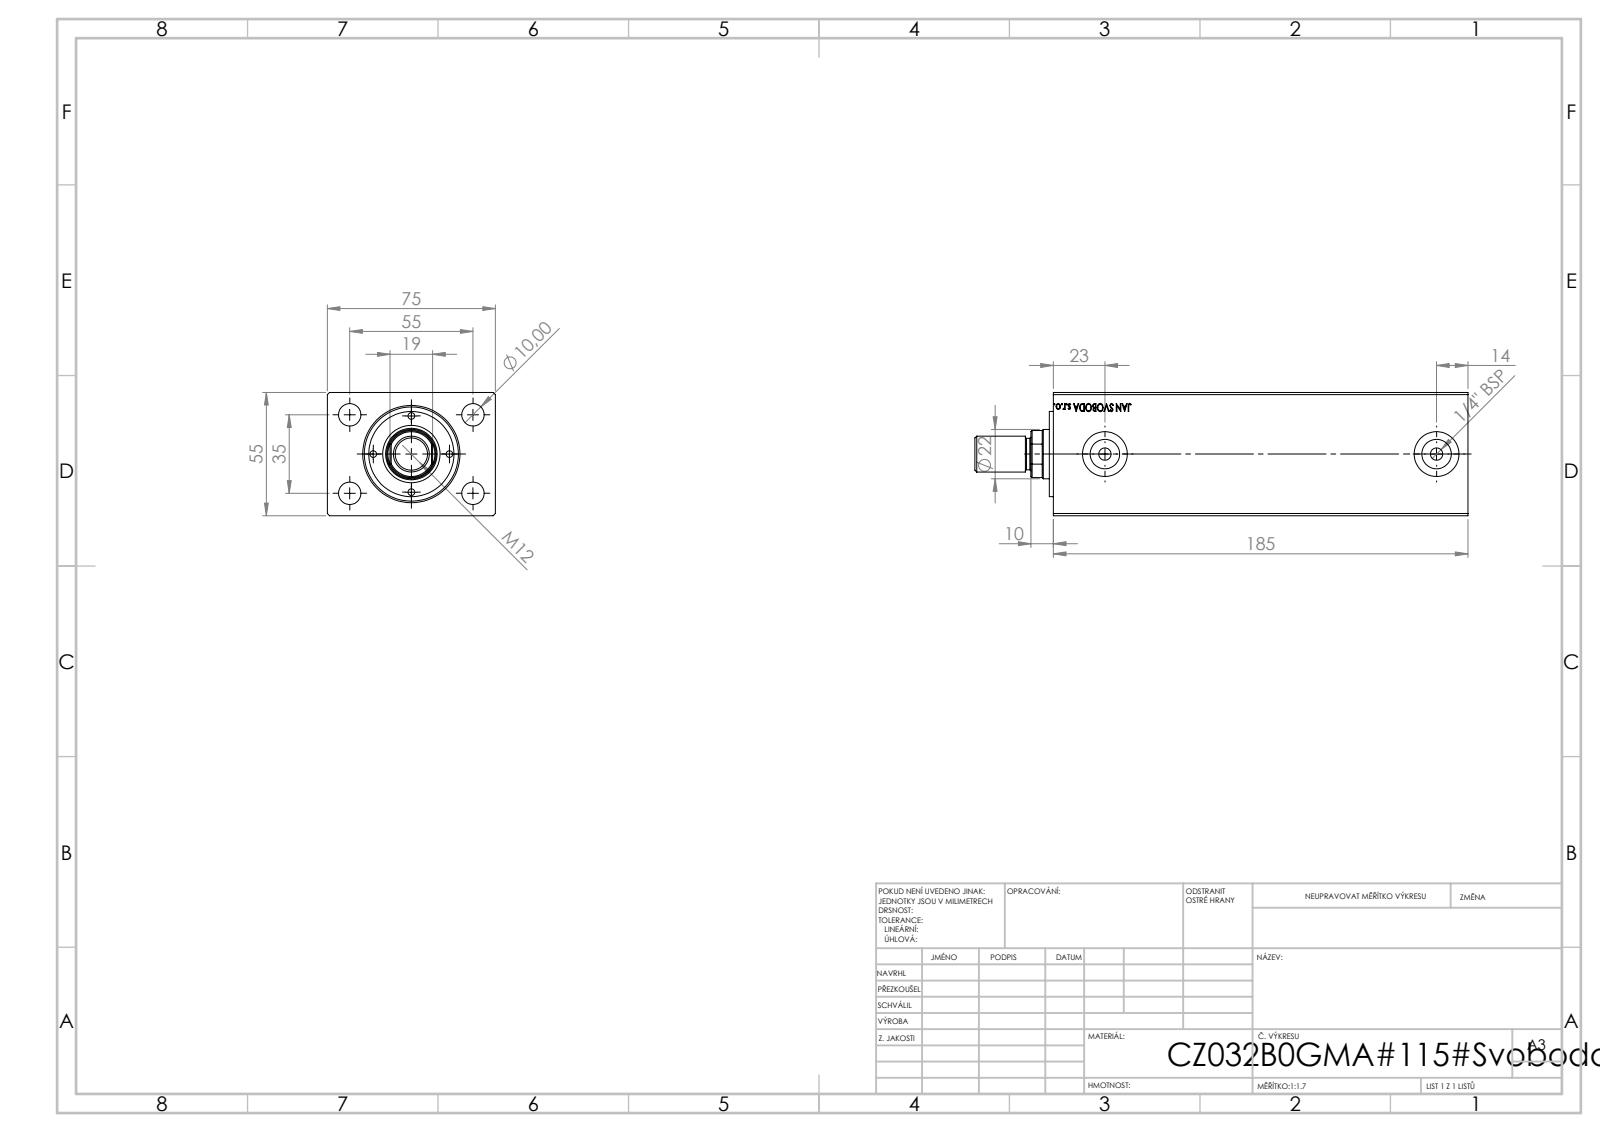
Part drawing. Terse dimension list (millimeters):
name: V500CZ; V500CZ_MALE_METRIC; V500CZ_B_VC
written by: SolidWorks 2019 (CONFIG_CONTROL_DESIGN)
unit: mm
bodies: 4 solids, 887 faces (403 planar, 62 cylindrical, 422 other)
size: 220 × 75 × 55
volume: 697 916 mm³; area: 102 760 mm²
holes: 4× ⌀3, 4× ⌀10, 2× ⌀5.5, 2× ⌀13.16, 2× ⌀20, 1× ⌀10.5, 1× ⌀22, 1× ⌀23, 1× ⌀32, 1× ⌀36, 1× ⌀42
bosses: 1× ⌀38, 1× ⌀16, 1× ⌀14
rounds: 1× R10.5
face distances: 55, 75, 185, 171.2, 13.8, 10, 8.2, 1.8, 184.8, 13.6
hole spacings: 17, 20.41, 24.04, 27.5, 32.6, 44.12, 47.82, 34
